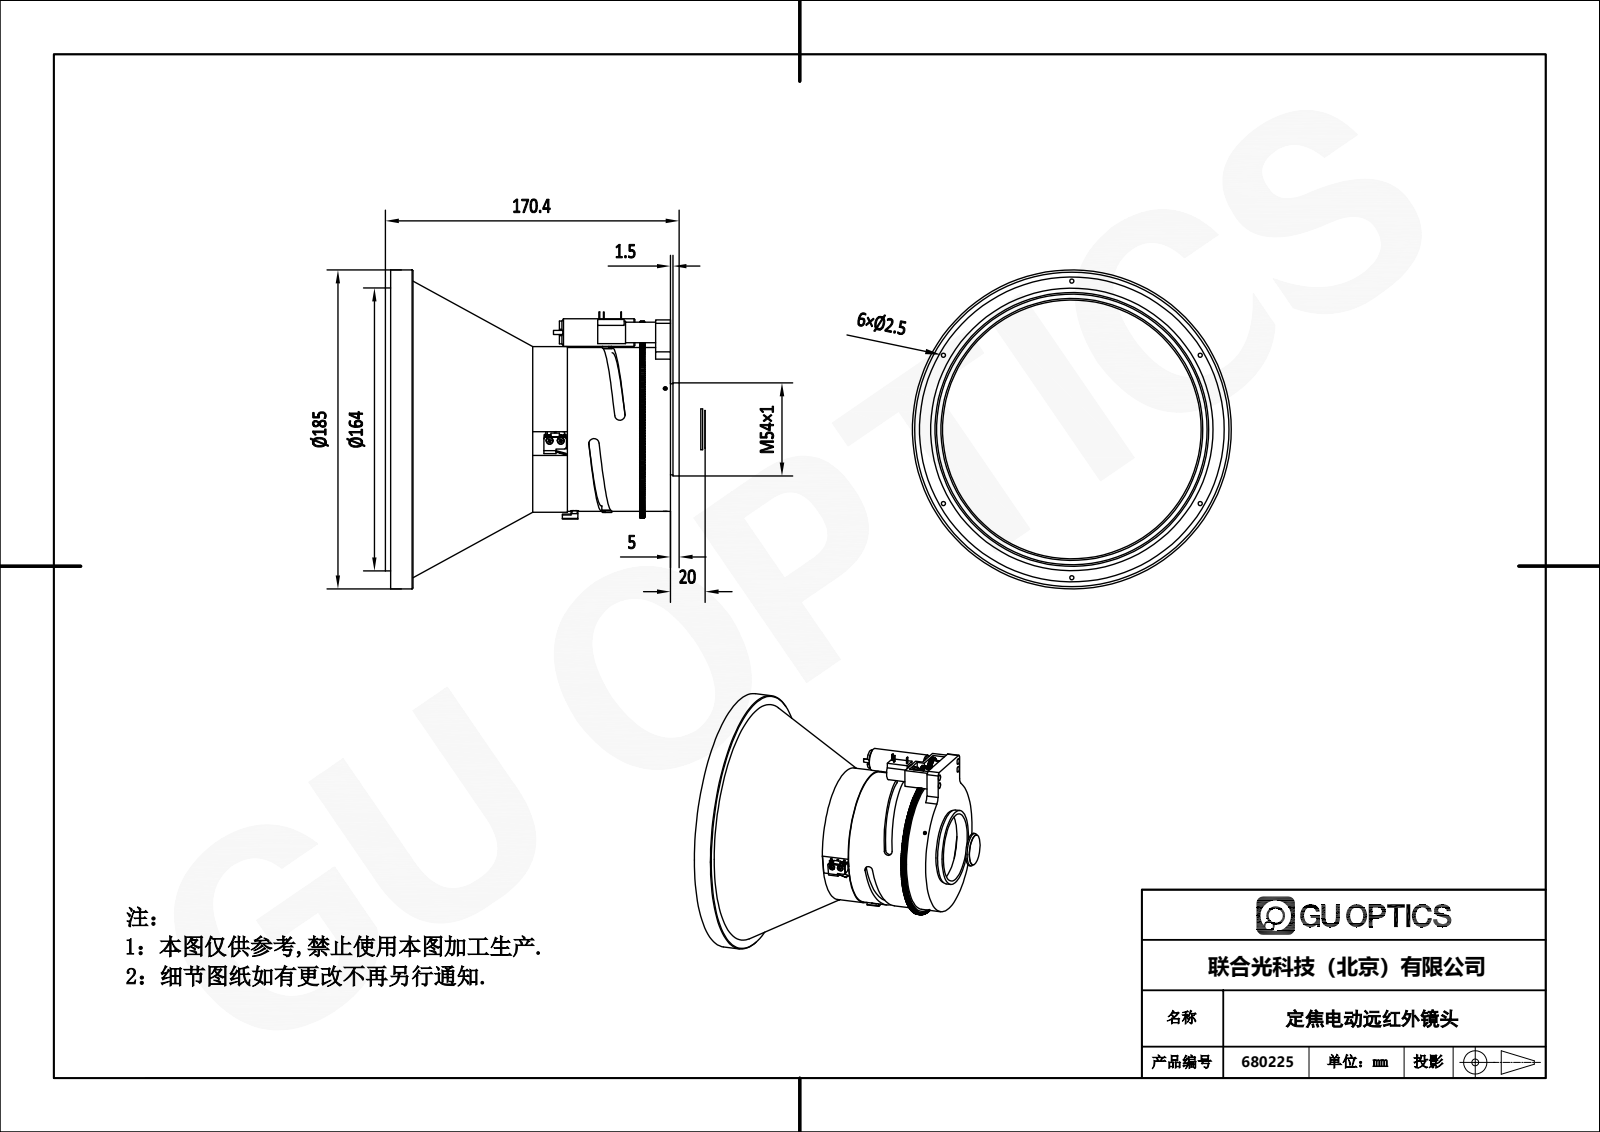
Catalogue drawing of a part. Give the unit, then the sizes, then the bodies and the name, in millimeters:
Units: millimetres
Overall size (bounding box): 185.46 × 185 × 185
Round holes (diameter × count): ⌀1.6 ×12, ⌀2.4 ×12, ⌀2.5 ×6, ⌀2.05 ×5, ⌀2 ×4, ⌀4.3 ×4, ⌀3 ×3, ⌀4 ×1, ⌀6.1 ×1, ⌀7 ×1, ⌀8 ×1, ⌀49 ×1
Round bosses / shafts (diameter × count): ⌀2 ×10, ⌀3.8 ×8, ⌀1.73 ×8, ⌀3 ×7, ⌀1.6 ×6, ⌀1.39 ×6, ⌀2.5 ×5, ⌀4 ×4
Partial cylindrical surfaces — rounded edges, fillets, slot ends (radius × count): R0.12 ×1008, R1.82 ×408, R3.28 ×96, R0.5 ×12, R1 ×12, R2 ×8, R0.55 ×2, R0.6 ×2
Main face-to-face distances: 3, 162.36, 14.86, 13, 147.5, 159.36, 146.36, 149.36, 144.5, 131.5
Hole centre spacings: 86, 6.5, 148.96, 8, 172, 5.06, 5.5, 6
Volume: 1 679 000 mm³ · Surface area: 157 958 mm²
Bodies: 47 solids, 3814 faces (821 planar, 2241 cylindrical, 752 other)
STEP written by: SolidWorks 2020 (CONFIG_CONTROL_DESIGN)
